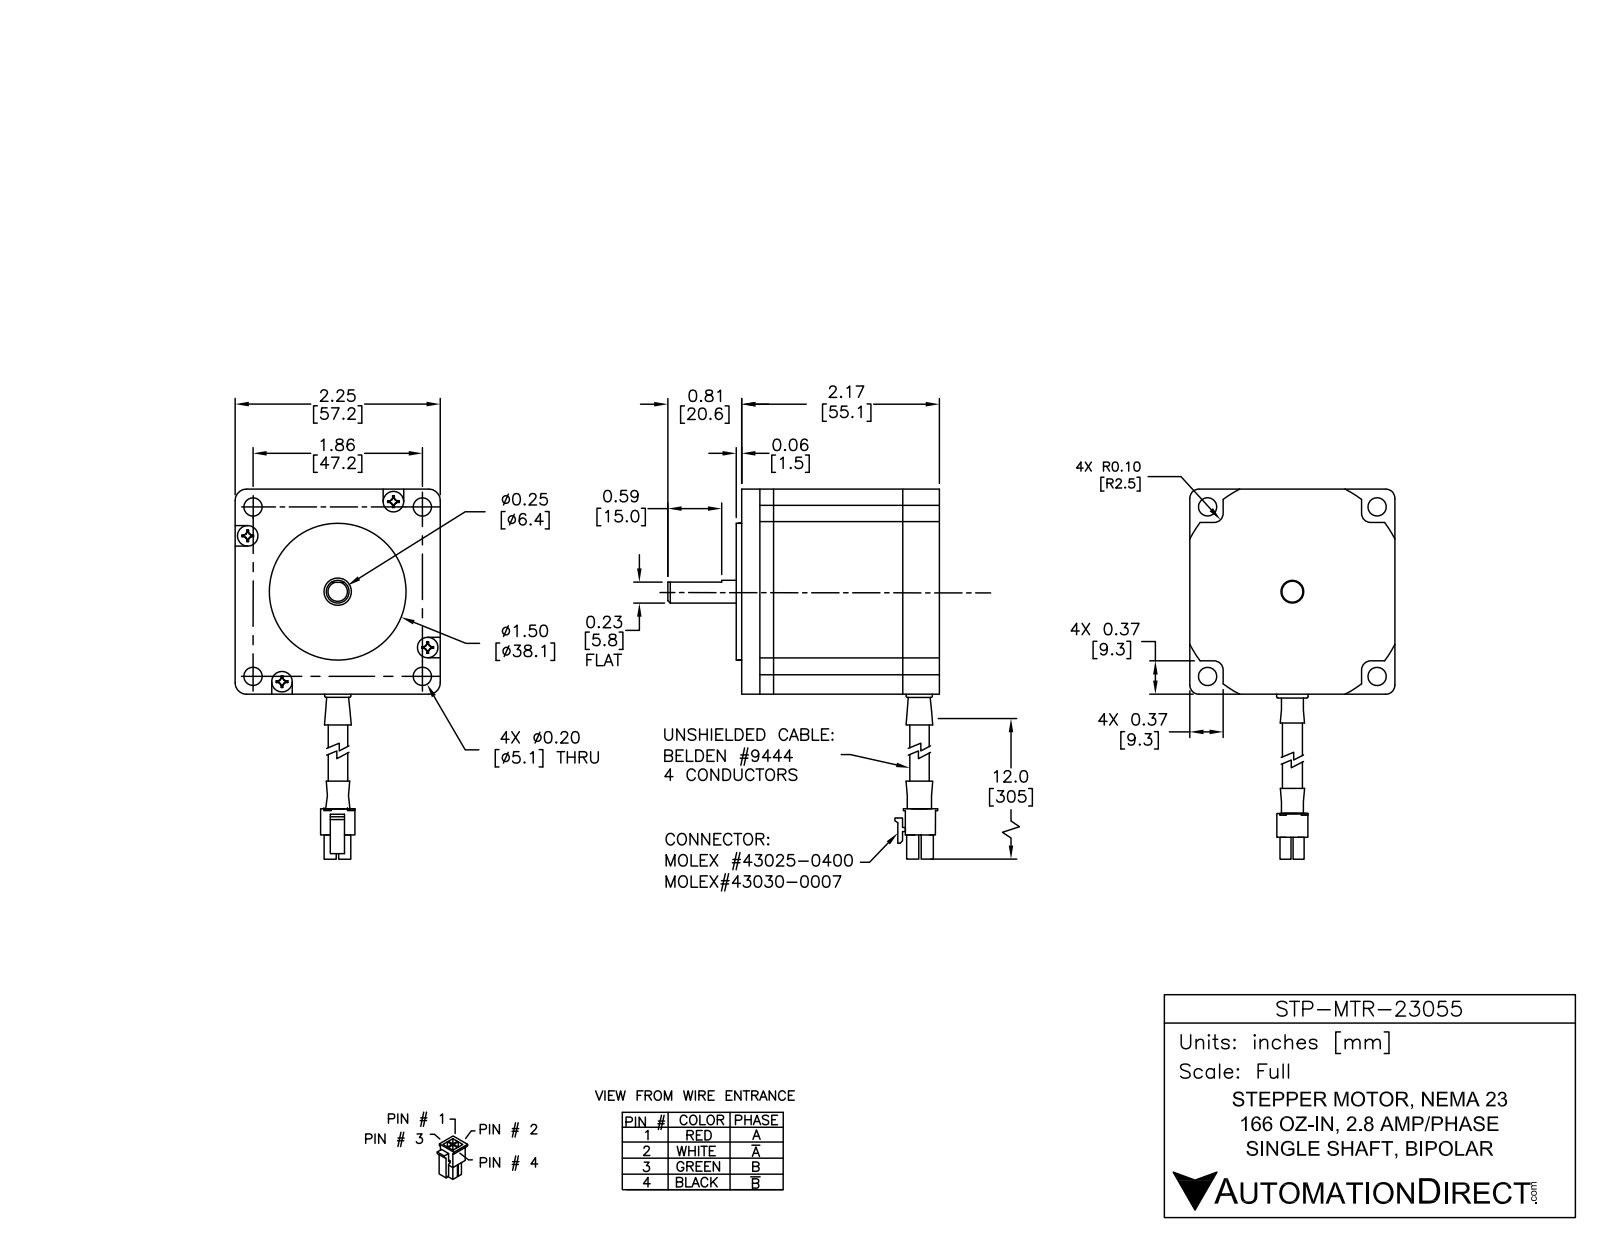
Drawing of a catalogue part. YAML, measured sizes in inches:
part_name: "STP-MTR-23055"
step_written_by: "SolidWorks 2014 (AUTOMOTIVE_DESIGN)"
units: inches
bodies: {solids: 17, faces: 1519, planar: 635, cylindrical: 751, other: 133}
overall_size: [14.207, 2.925, 2.207]
volume: 6.793
surface_area: 102.5
round_holes:
  - {diameter: 0.2, count: 5}
  - {diameter: 0.097, count: 4}
  - {diameter: 0.118, count: 4}
  - {diameter: 0.063, count: 1}
  - {diameter: 0.295, count: 1}
  - {diameter: 0.394, count: 1}
  - {diameter: 0.394, count: 1}
  - {diameter: 0.398, count: 1}
  - {diameter: 0.45, count: 1}
  - {diameter: 0.474, count: 1}
  - {diameter: 0.65, count: 1}
  - {diameter: 0.7, count: 1}
round_bosses_or_shafts:
  - {diameter: 0.205, count: 4}
  - {diameter: 0.126, count: 4}
  - {diameter: 0.125, count: 4}
  - {diameter: 0.05, count: 4}
  - {diameter: 1.5, count: 1}
  - {diameter: 1.44, count: 1}
  - {diameter: 1.375, count: 1}
  - {diameter: 1.372, count: 1}
partial_cylinders:
  - {radius: 0.025, count: 100}
  - {radius: 0.03, count: 46}
  - {radius: 0.02, count: 40}
  - {radius: 0.012, count: 8}
  - {radius: 0.14, count: 8}
  - {radius: 0.039, count: 4}
  - {radius: 0.062, count: 4}
  - {radius: 0.125, count: 4}
face_to_face_distances: [2.207, 0.048, 1.978, 0.865, 1.065, 0.913, 1.113, 0.139, 2.069, 1.93]
hole_center_spacings: [0.315, 0.316, 1.159, 1.16, 1.236, 1.314, 1.548, 1.548]
